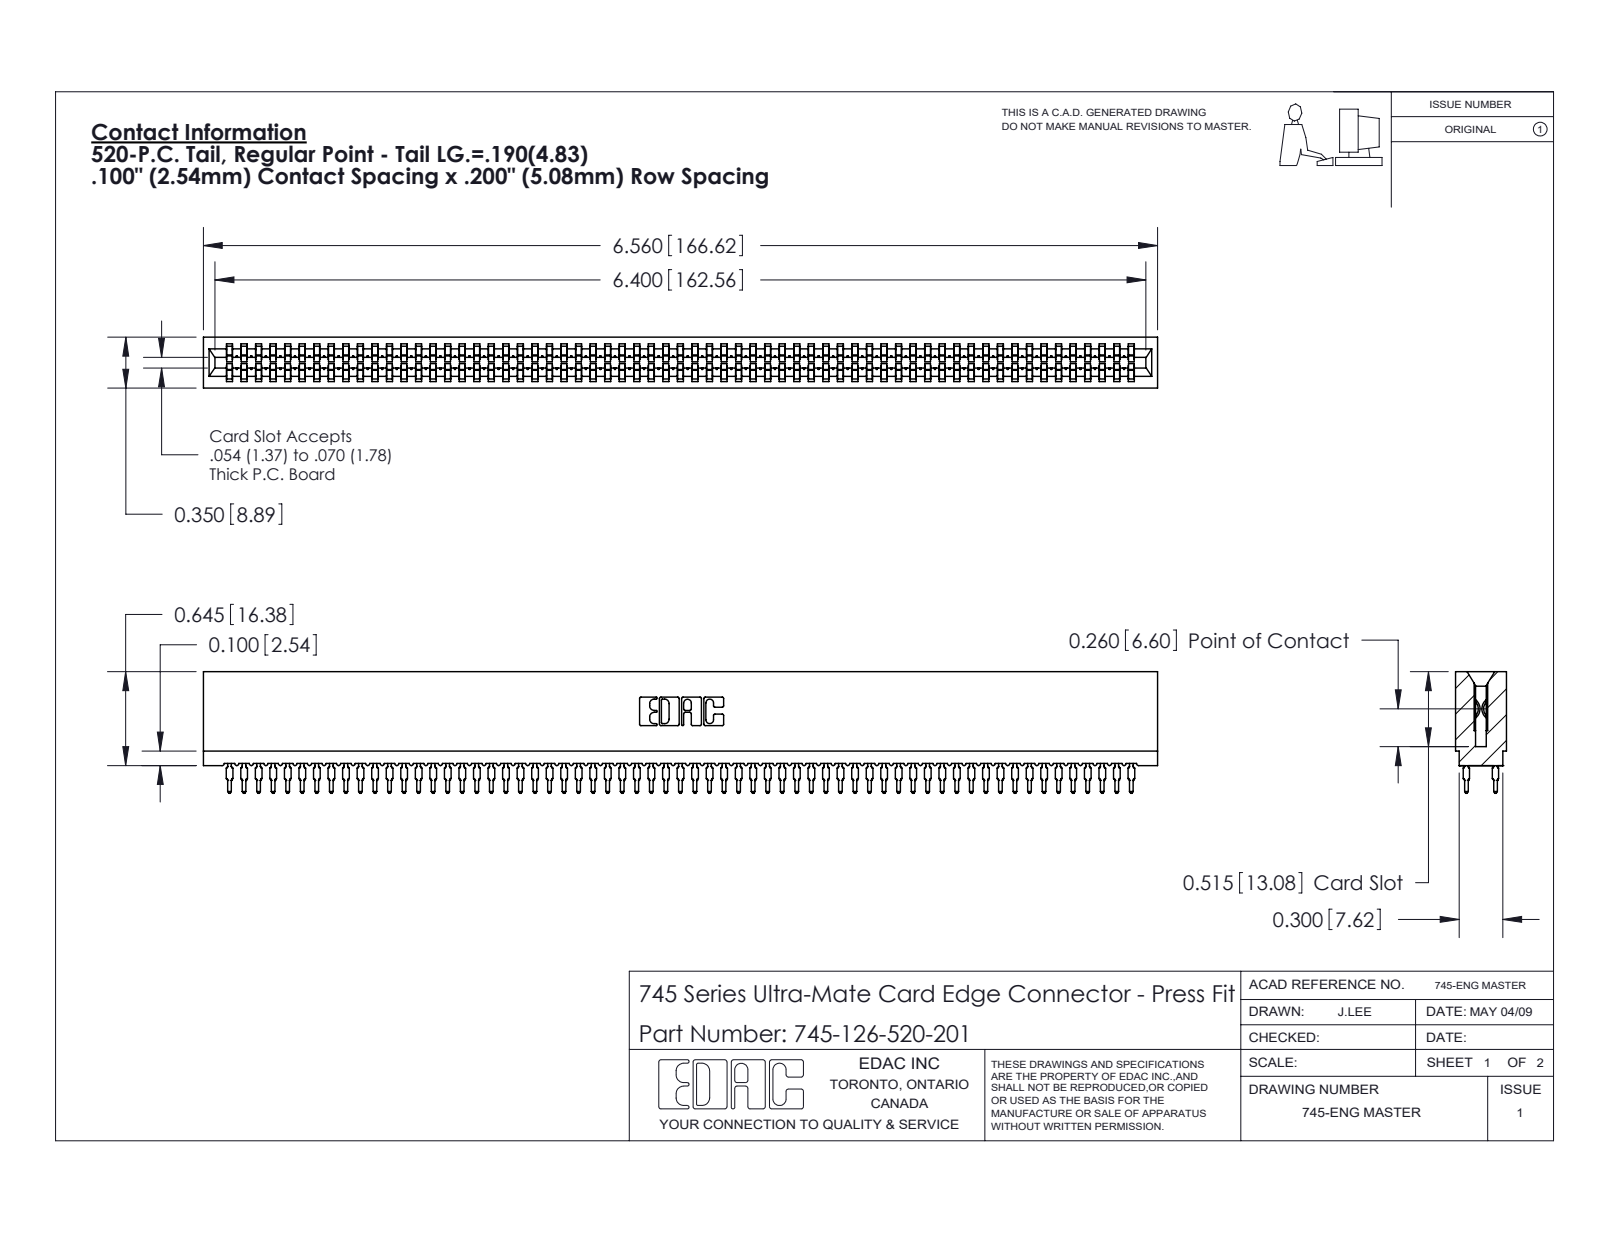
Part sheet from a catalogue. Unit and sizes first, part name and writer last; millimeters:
Units: millimetres
Overall size (bounding box): 166.6 × 21.2 × 8.9
Partial cylindrical surfaces — rounded edges, fillets, slot ends (radius × count): R0.5 ×252, R0.4 ×126, R0.3 ×22, R0.1 ×8, R0.3 ×8, R0.2 ×6, R0.8 ×6, R0.7 ×3
Main face-to-face distances: 8.9, 1.6, 7.3, 1.1, 7.7, 0.5, 6.2, 3.5, 5.4, 2.4
Volume: 14 800 mm³ · Surface area: 29 940 mm²
Bodies: 127 solids, 11372 faces (5851 planar, 2245 cylindrical, 3276 other)
Part name (STEP PRODUCT): 745-292-001_520; 745 Part_Insulator Option - 01; 745-126-520-201
STEP written by: SolidWorks 2020 (CONFIG_CONTROL_DESIGN)
